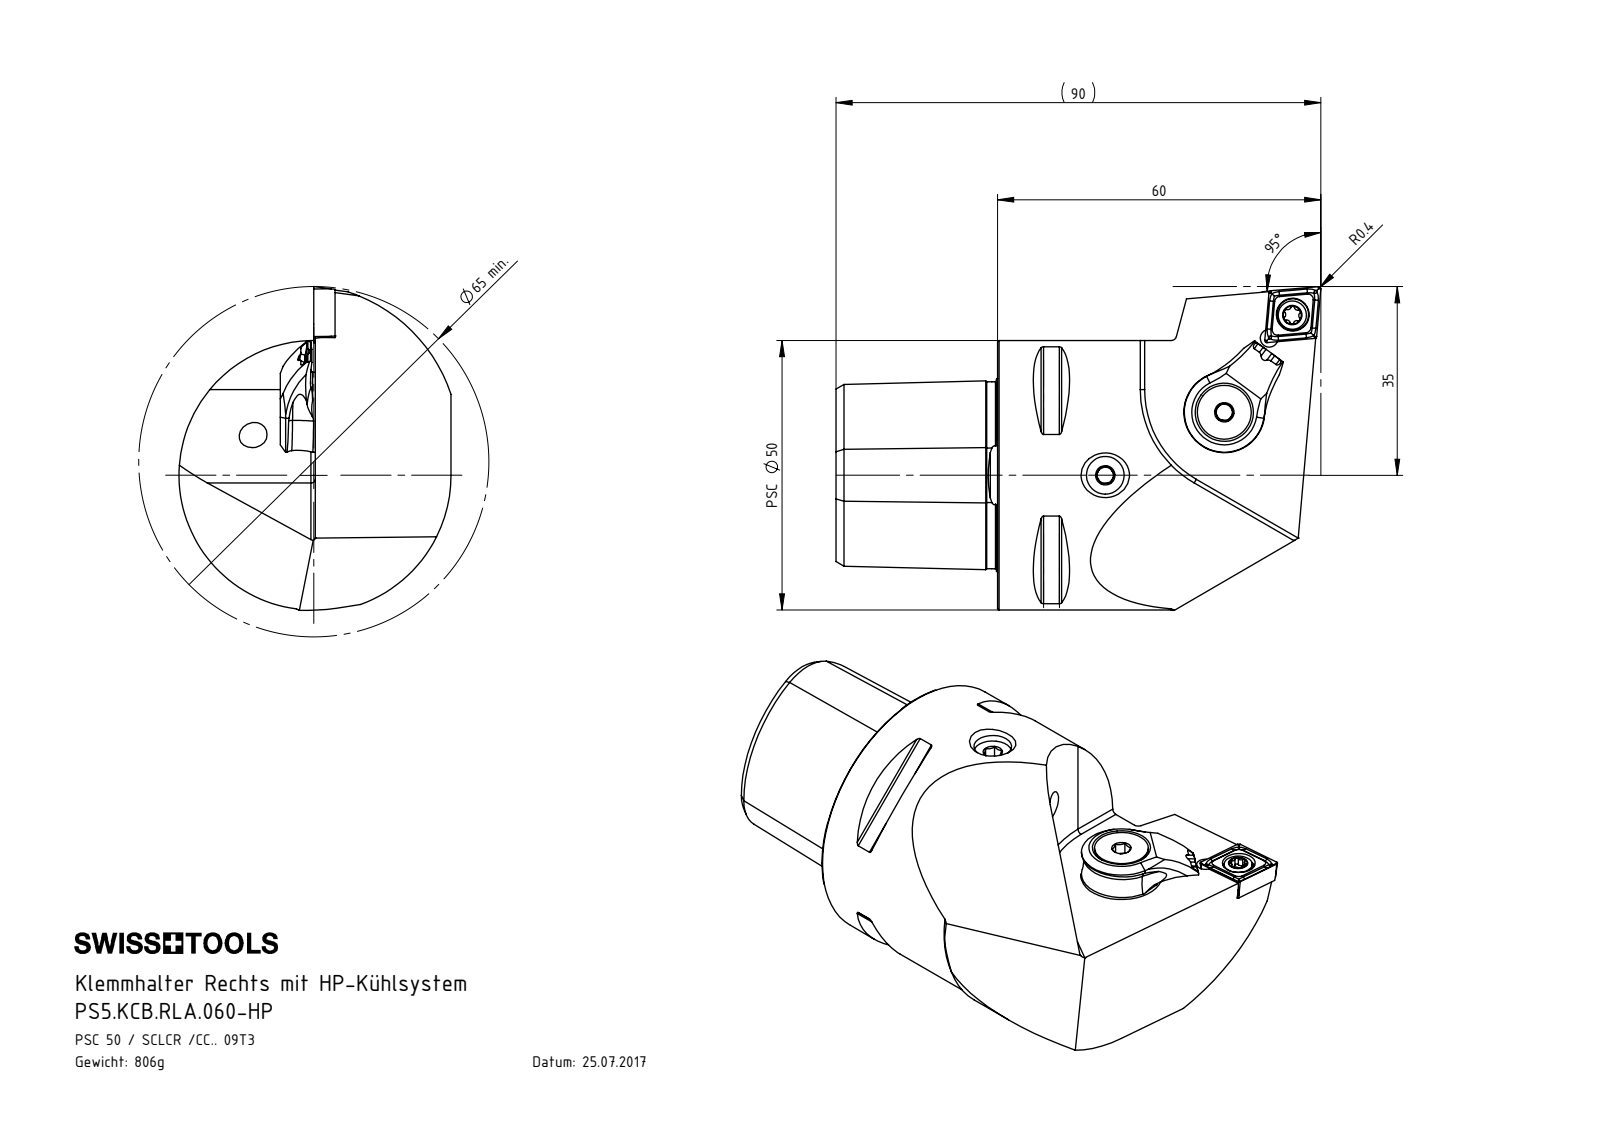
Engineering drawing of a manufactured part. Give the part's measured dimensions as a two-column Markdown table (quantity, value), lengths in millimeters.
| quantity | value |
| --- | --- |
| part name | PS5.KCB.RLA.060-HP; CHP-ER1.008.014_A; DIN 3771 - 13x1; DIN 7991 - M5x18 (+7 more) |
| STEP written by | SolidWorks 2022 (AUTOMOTIVE_DESIGN) |
| units | millimeters |
| bodies | 9 solids, 484 faces (101 planar, 134 cylindrical, 249 other) |
| overall size | 90 × 60.05 × 50.5 |
| volume | 103 119 mm³ |
| surface area | 23 278 mm² |
| round holes (diameter × count) | 3.3 × 2, 4.2 × 2, 5 × 2, 6.1 × 2, 1.2 × 1, 2 × 1, 3 × 1, 4 × 1, 4.4 × 1, 5.3 × 1, 7 × 1, 8.4 × 1 |
| round bosses / shafts (diameter × count) | 50 × 1, 14.85 × 1, 13.4 × 1, 10 × 1, 8 × 1, 5.5 × 1, 5.25 × 1, 5 × 1 |
| partial cylindrical surfaces (radius × count) | 0.5 × 10, 1 × 7, 0.34 × 6, 0.59 × 6, 6 × 3, 0.8 × 2, 1.1 × 2, 1.2 × 2 |
| main face-to-face distances | 30, 25.2, 19.18, 20.7, 4.5, 44.4, 1.5, 3, 56.5, 26.5 |
| hole center spacings | 34, 4.5, 6.07, 6.19, 8, 12.56, 16.06, 18.62 |
